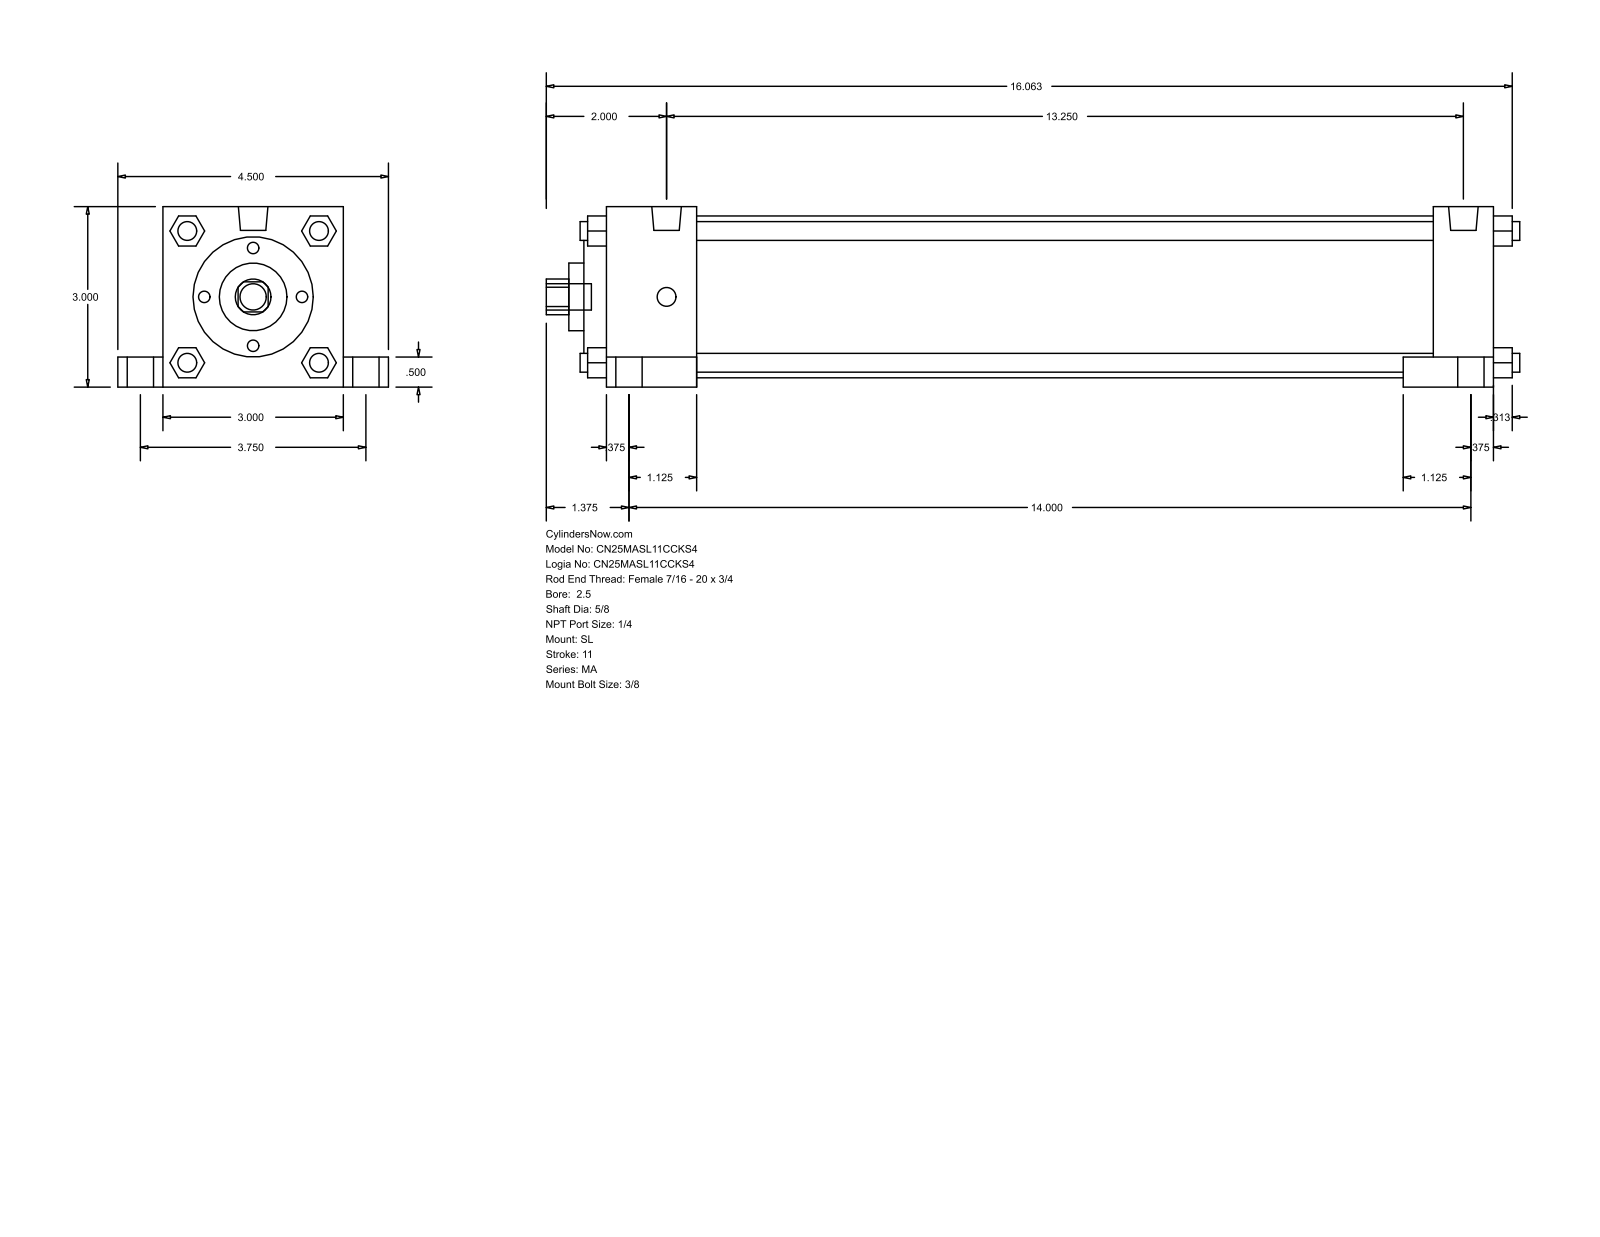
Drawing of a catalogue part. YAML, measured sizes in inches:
part_name: "MA_SL__0250_0.625"
step_written_by: "GSSL Pune (CONFIG_CONTROL_DESIGN)"
units: inches
bodies: {solids: 0, faces: 150, planar: 113, cylindrical: 37, other: 0}
overall_size: [16.187, 4.5, 3]
round_holes:
  - {diameter: 0.625, count: 1}
  - {diameter: 1.125, count: 1}
  - {diameter: 2, count: 1}
  - {diameter: 2.69, count: 1}
round_bosses_or_shafts:
  - {diameter: 0.313, count: 8}
  - {diameter: 0.437, count: 5}
  - {diameter: 0.687, count: 4}
  - {diameter: 0.492, count: 2}
partial_cylinders:
  - {radius: 0.297, count: 1}
face_to_face_distances: [3, 14.75, 0.5, 12.25, 1, 1.5, 13.25, 13.75, 0.75, 2.5]
